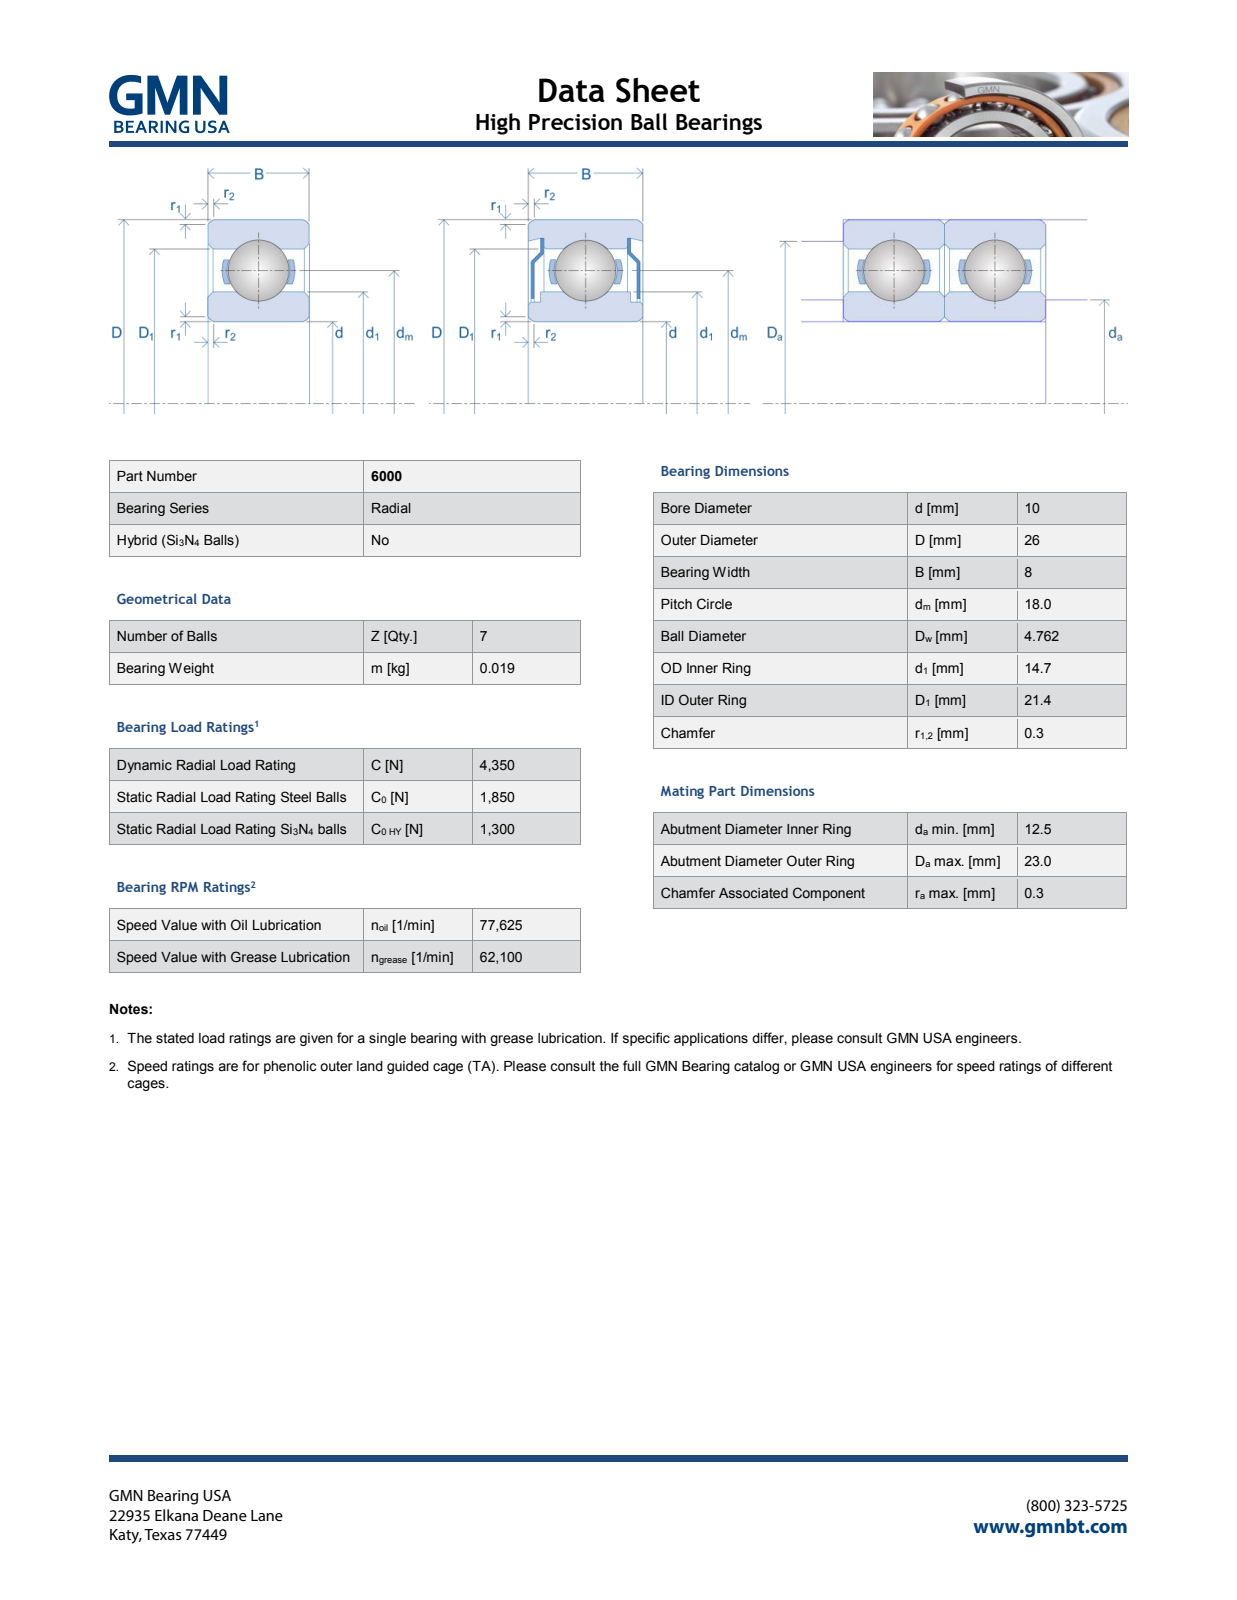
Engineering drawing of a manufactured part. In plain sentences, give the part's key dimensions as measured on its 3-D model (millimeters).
The part is named "6000_PRT". Its 3-D file was written by "PRO/ENGINEER BY PARAMETRIC TECHNOLOGY CORPORATION, 2013150 (AUTOMOTIVE_DESIGN)". It is 10 solids with 544 faces: 480 planar, 30 cylindrical and 34 other. Overall it measures 26 by 26 by 8.01 millimeters. Its volume is 2 786 cubic millimeters and its surface area 3 814 square millimeters. Round holes: 7 of diameter 4.96, 1 of diameter 10, 1 of diameter 17.6, 1 of diameter 21.4. Round bosses or shafts: 1 of diameter 26, 1 of diameter 20.6, 1 of diameter 14.65. The main face-to-face distances are 8, 7.9, 7.8, 7.91, 8.01, 1.3, 1.14, 1.13, 0.92, 0.97.
